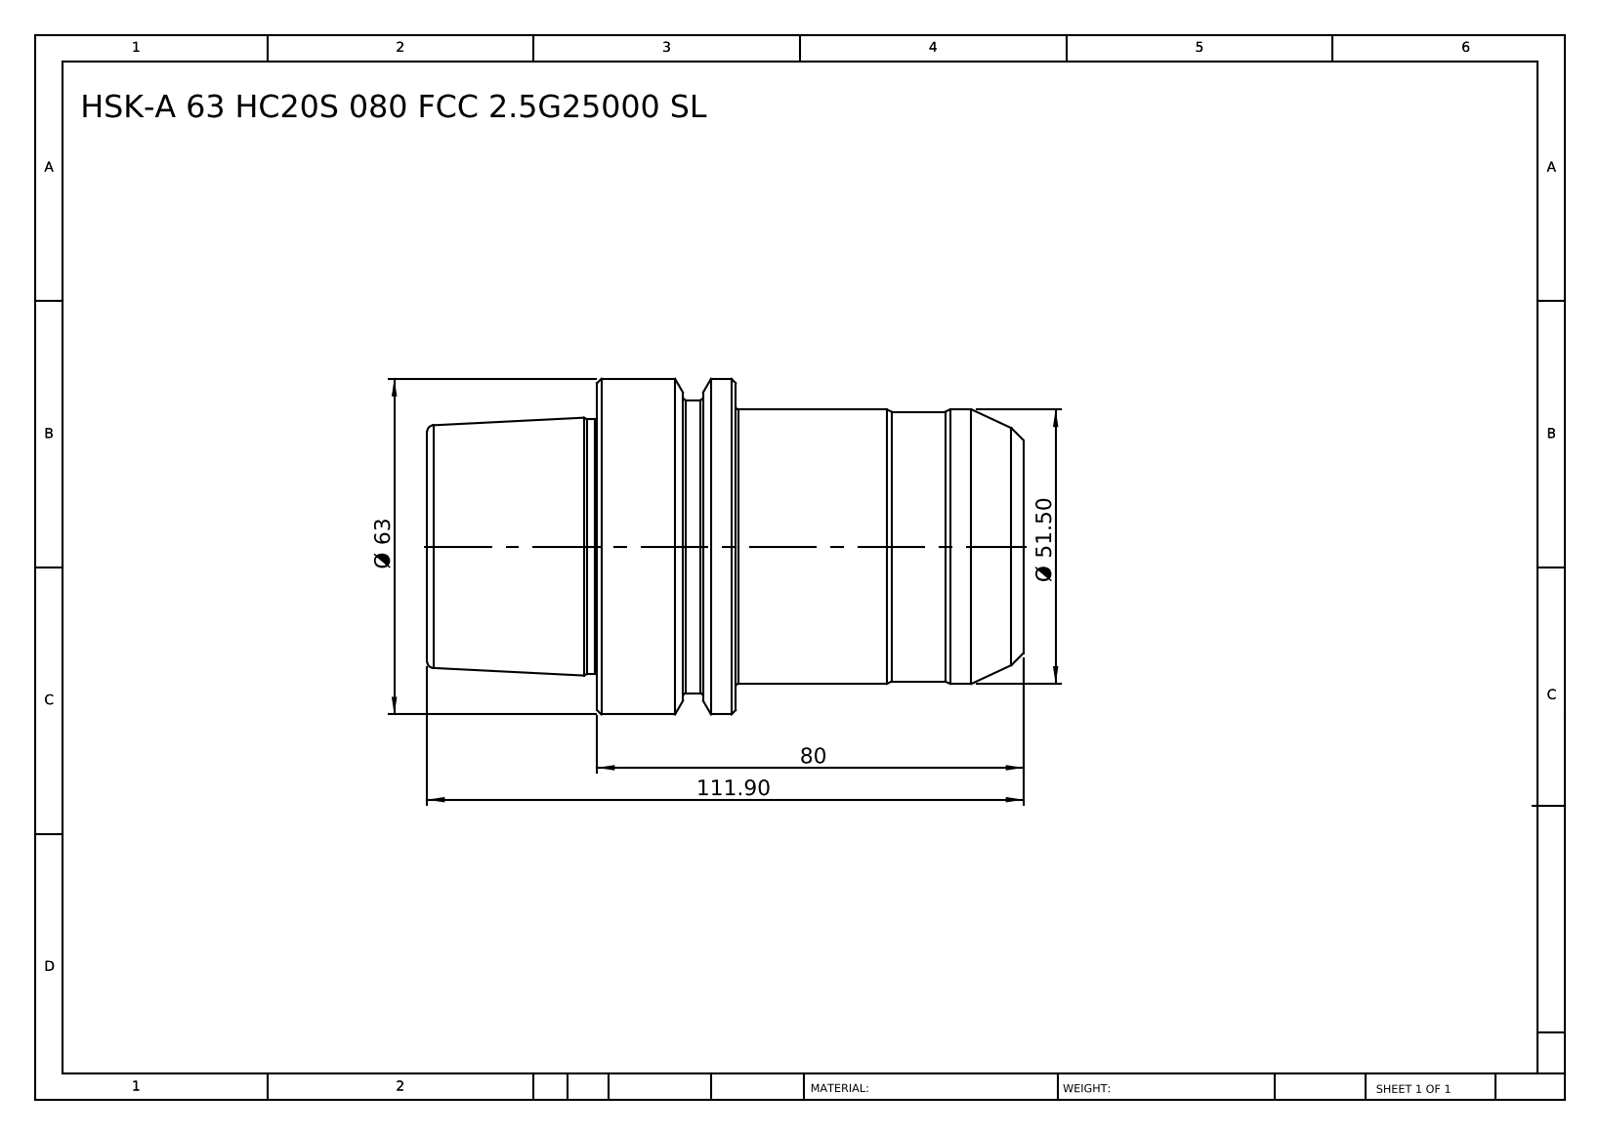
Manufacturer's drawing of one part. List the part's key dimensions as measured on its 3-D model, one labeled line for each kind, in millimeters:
Part name (STEP PRODUCT): HSK-A 63 HC20S 080 FCC 2.5G25000 SL
STEP written by: SolidWorks 2014 (CONFIG_CONTROL_DESIGN)
Units: millimetres
Bodies: 1 solid, 52 faces (6 planar, 14 cylindrical, 32 other)
Overall size (bounding box): 111.9 × 63 × 63
Volume: 240 827 mm³ · Surface area: 24 509 mm²
Round bosses / shafts (diameter × count): ⌀63 ×1, ⌀55 ×1, ⌀51.5 ×1, ⌀50.6 ×1, ⌀47.78 ×1
Main face-to-face distances: 111.9, 80, 31.9, 54, 26, 57.9, 60.1, 6.1, 19.9, 51.8
